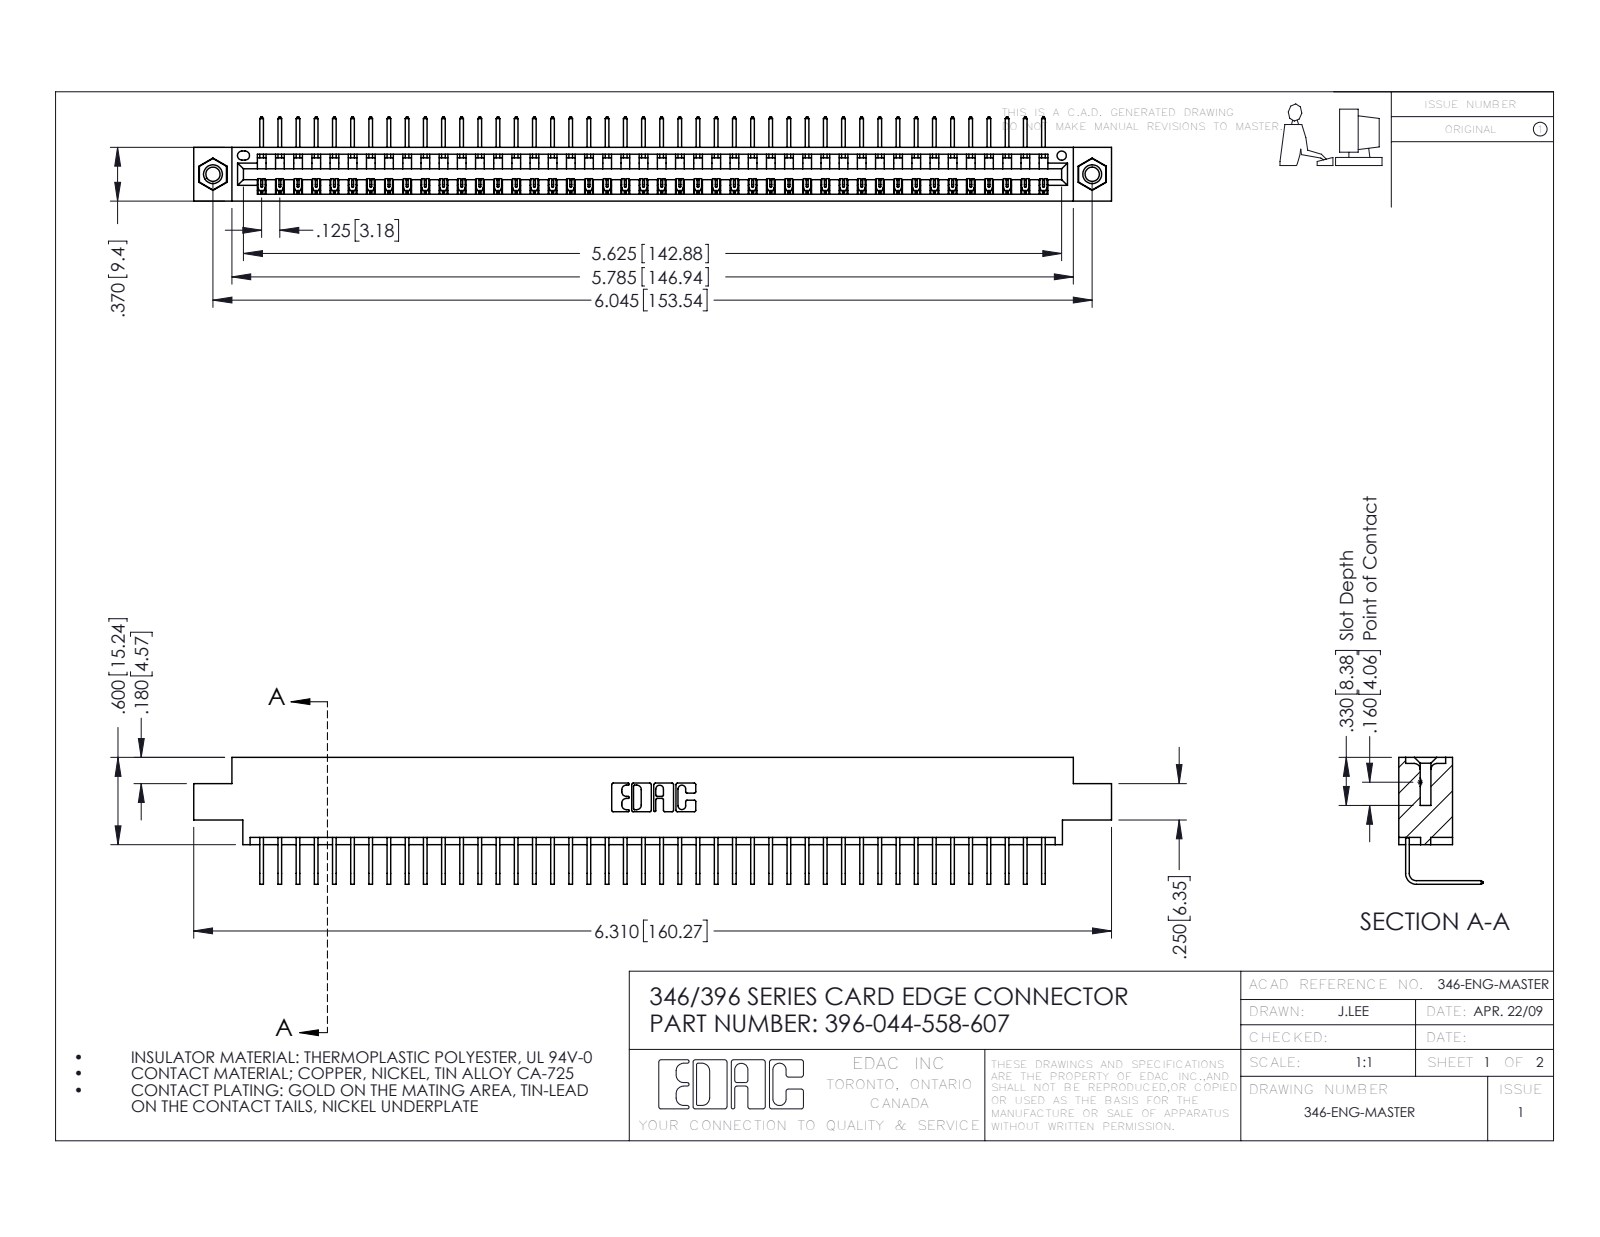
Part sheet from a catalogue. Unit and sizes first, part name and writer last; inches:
Units: inches
Overall size (bounding box): 6.31 × 0.873 × 0.58
Round holes (diameter × count): ⌀0.098 ×2, ⌀0.125 ×2, ⌀0.156 ×2, ⌀0.064 ×1
Round bosses / shafts (diameter × count): ⌀0.155 ×2
Partial cylindrical surfaces — rounded edges, fillets, slot ends (radius × count): R0.006 ×88, R0.01 ×22, R0.007 ×6, R0.031 ×6, R0.026 ×3, R0.031 ×2, R0.04 ×2, R0.014 ×1
Main face-to-face distances: 0.322, 0.048, 0.37, 0.25, 0.298, 0.025, 0.072, 0.222, 0.148, 0.1
Hole centre spacings: 0.246, 5.836, 6.045
Volume: 0.936 in³ · Surface area: 31.4 in²
Bodies: 47 solids, 2826 faces (1960 planar, 850 cylindrical, 16 other)
Part name (STEP PRODUCT): 396-044-558-607; 346 Part_0.170 Offset - 0.156 Dia-TI; 345-292-001_558 Tail - 2; 345-250-001_345-250-005-103
STEP written by: SolidWorks 2016 (CONFIG_CONTROL_DESIGN)
